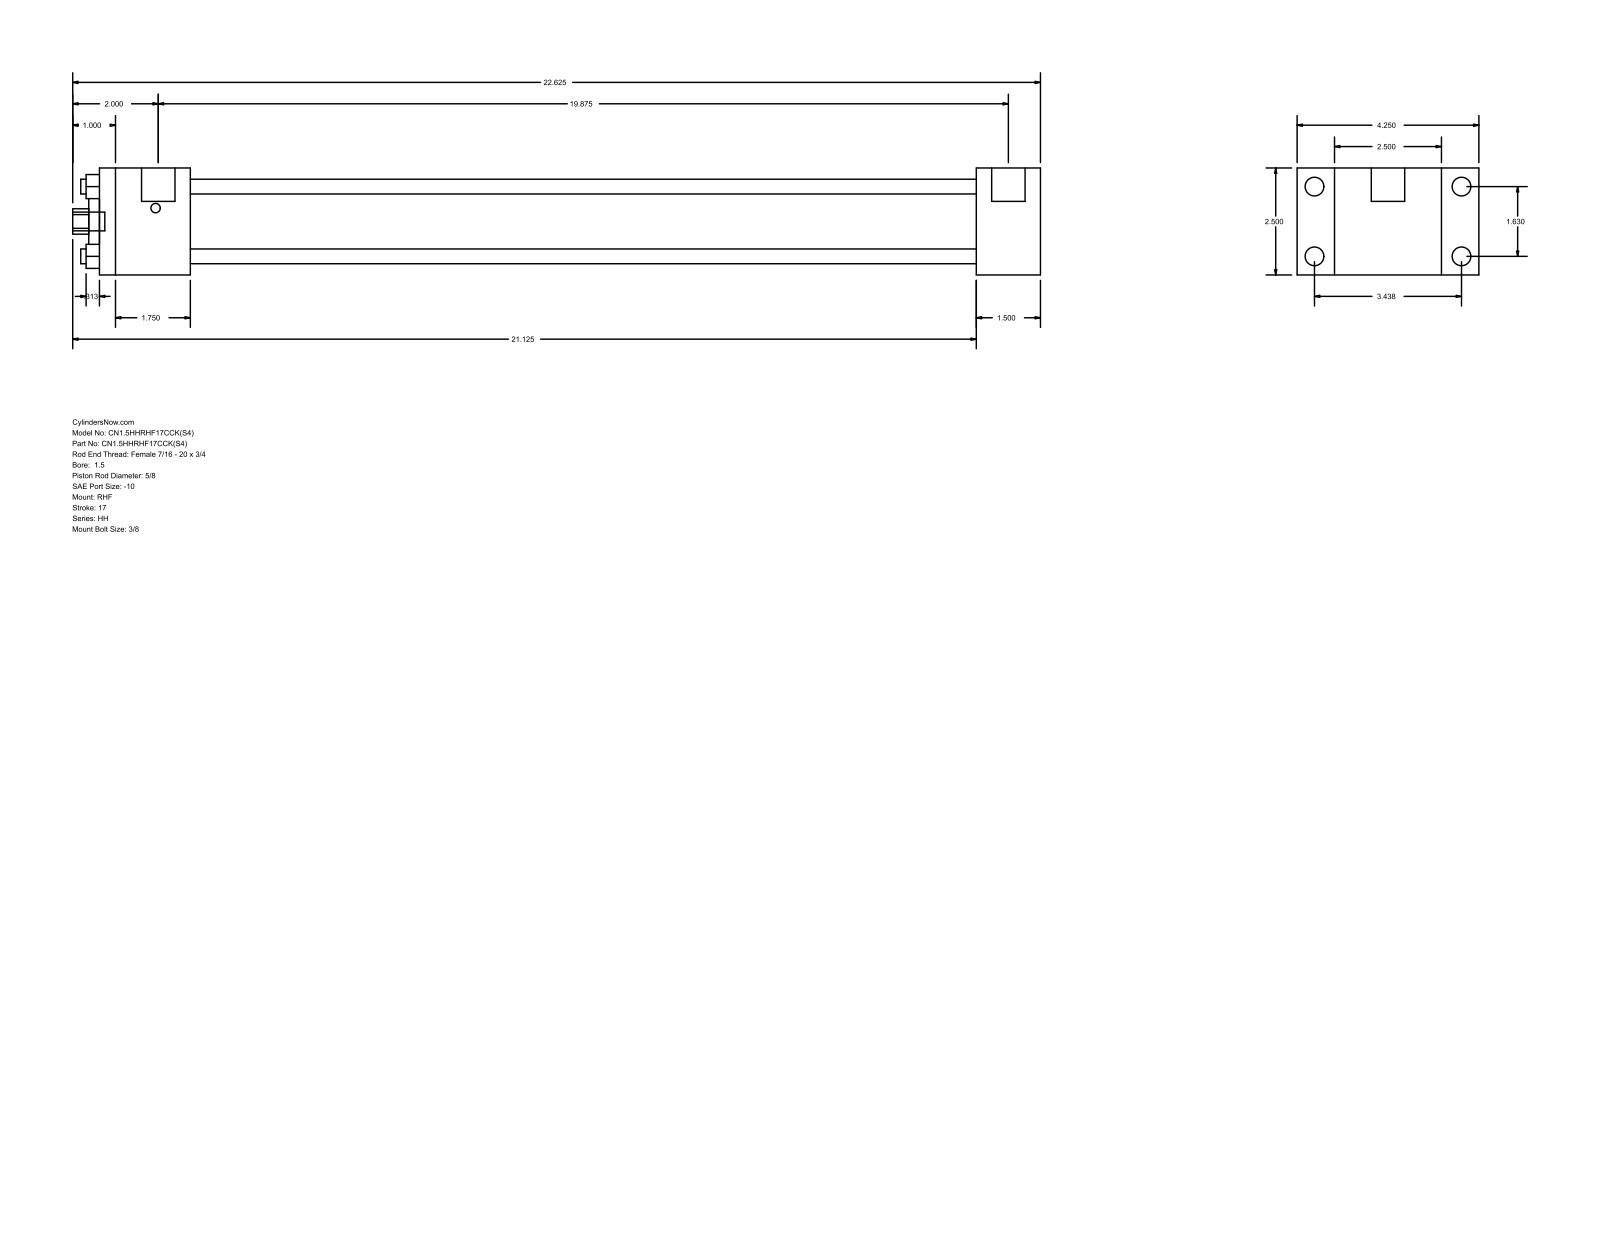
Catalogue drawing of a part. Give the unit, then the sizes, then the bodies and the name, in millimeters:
Units: millimetres
Overall size (bounding box): 574.67 × 107.95 × 63.5
Round holes (diameter × count): ⌀8.76 ×4, ⌀15.88 ×1, ⌀28.57 ×1, ⌀44.45 ×1
Round bosses / shafts (diameter × count): ⌀11.13 ×4, ⌀5.56 ×4, ⌀19.84 ×2, ⌀11.11 ×1
Partial cylindrical surfaces — rounded edges, fillets, slot ends (radius × count): R7.54 ×1
Main face-to-face distances: 63.5, 22.23, 85.73, 38.09, 520.7, 558.79, 107.96, 53.97, 466.73, 504.82
Hole centre spacings: 29.27, 41.4, 58.55
Bodies: 0 solids, 88 faces (60 planar, 28 cylindrical, 0 other)
Part name (STEP PRODUCT): HH_RHF__0150_0.625
STEP written by: GSSL Pune (CONFIG_CONTROL_DESIGN)
